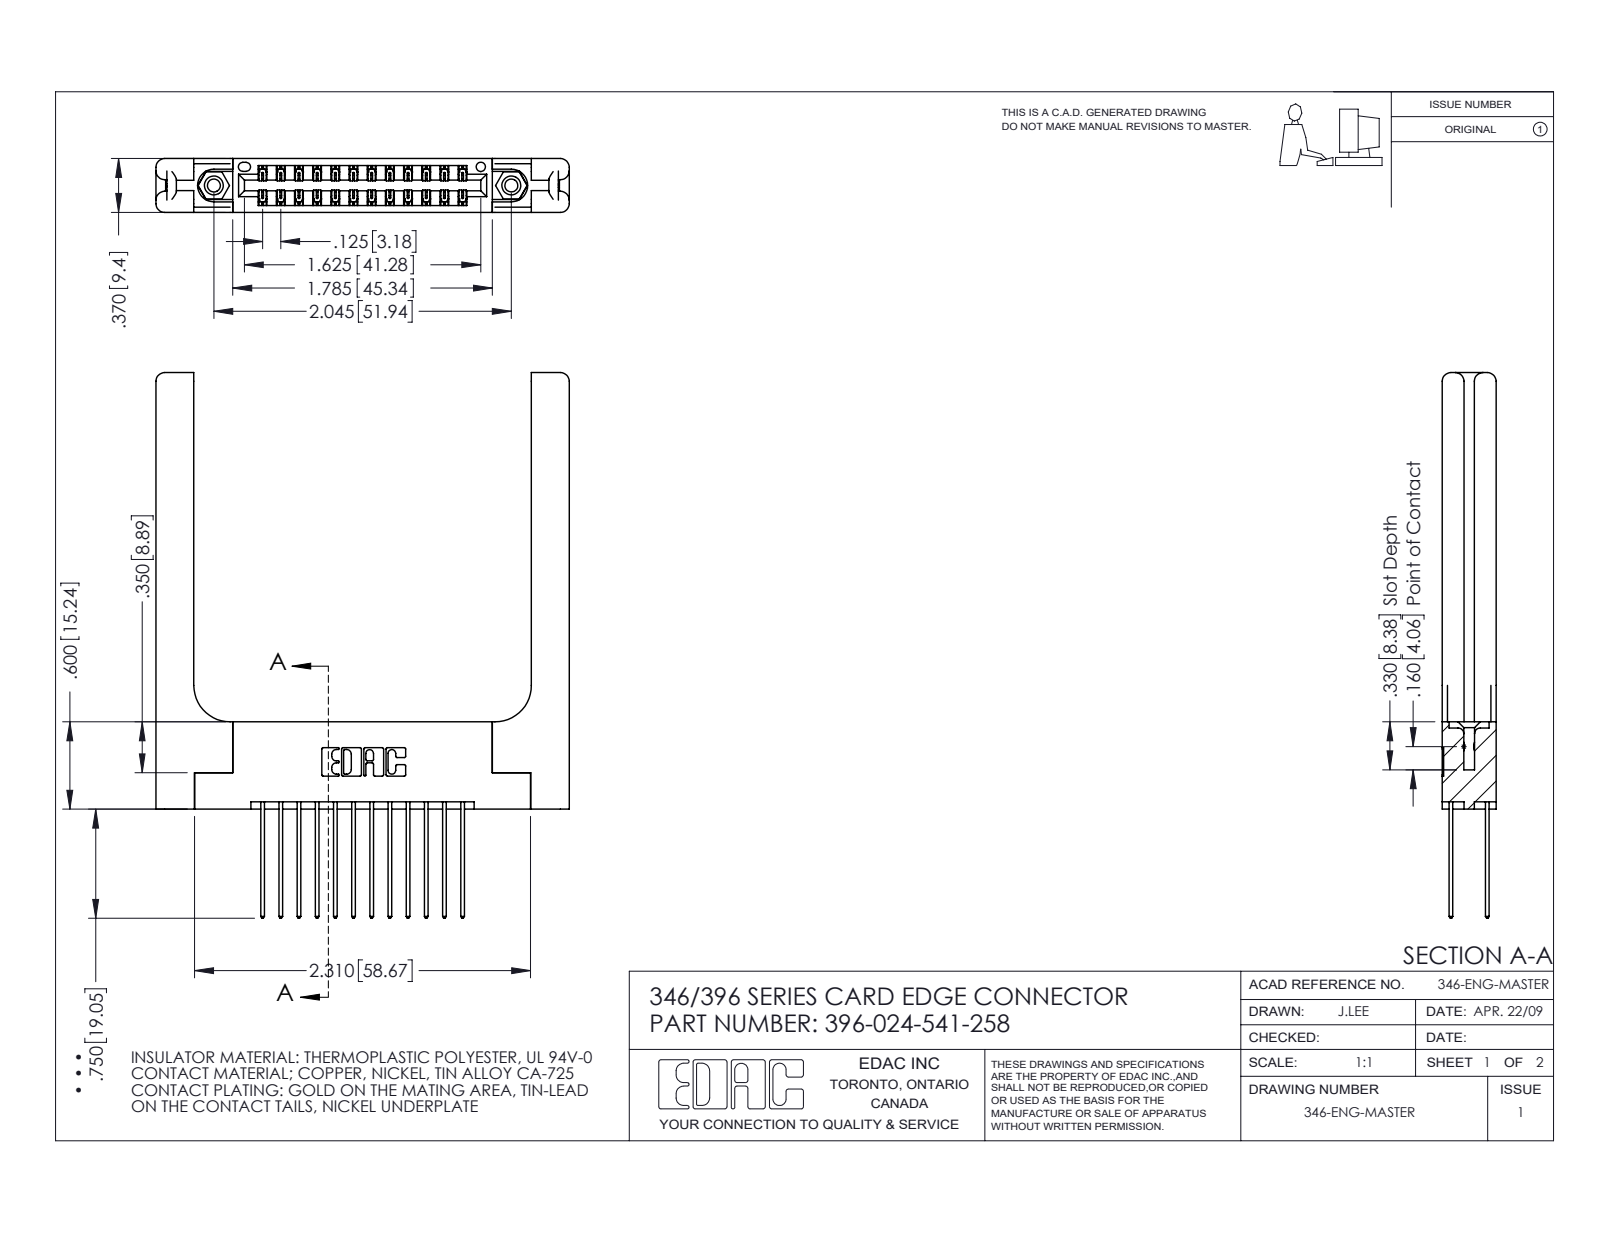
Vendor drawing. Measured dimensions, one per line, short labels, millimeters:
name: 396-024-541-258; 346-220-058_345-220-058; 345-250-001_345-250-001-102; 346 Part_Flush Mounting Lugs - 0.156 Dia-TH (+1 more)
written by: SolidWorks 2016 (CONFIG_CONTROL_DESIGN)
unit: mm
bodies: 29 solids, 1626 faces (1064 planar, 502 cylindrical, 60 other)
size: 95.3 × 72.2 × 9.4
volume: 14 400 mm³; area: 14 700 mm²
holes: 2× ⌀2.3, 2× ⌀3.2, 2× ⌀4, 1× ⌀1.6
bosses: 2× ⌀3.9
rounds: 36× R0.2, 24× R0.3, 22× R0.3, 16× R1.5, 6× R0.2, 6× R0.8, 3× R0.7, 2× R0.4
face distances: 9.4, 1.8, 3.8, 3.8, 1.2, 8.2, 6.4, 0.6, 2, 7.6
hole spacings: 6.2, 46.7, 51.9
